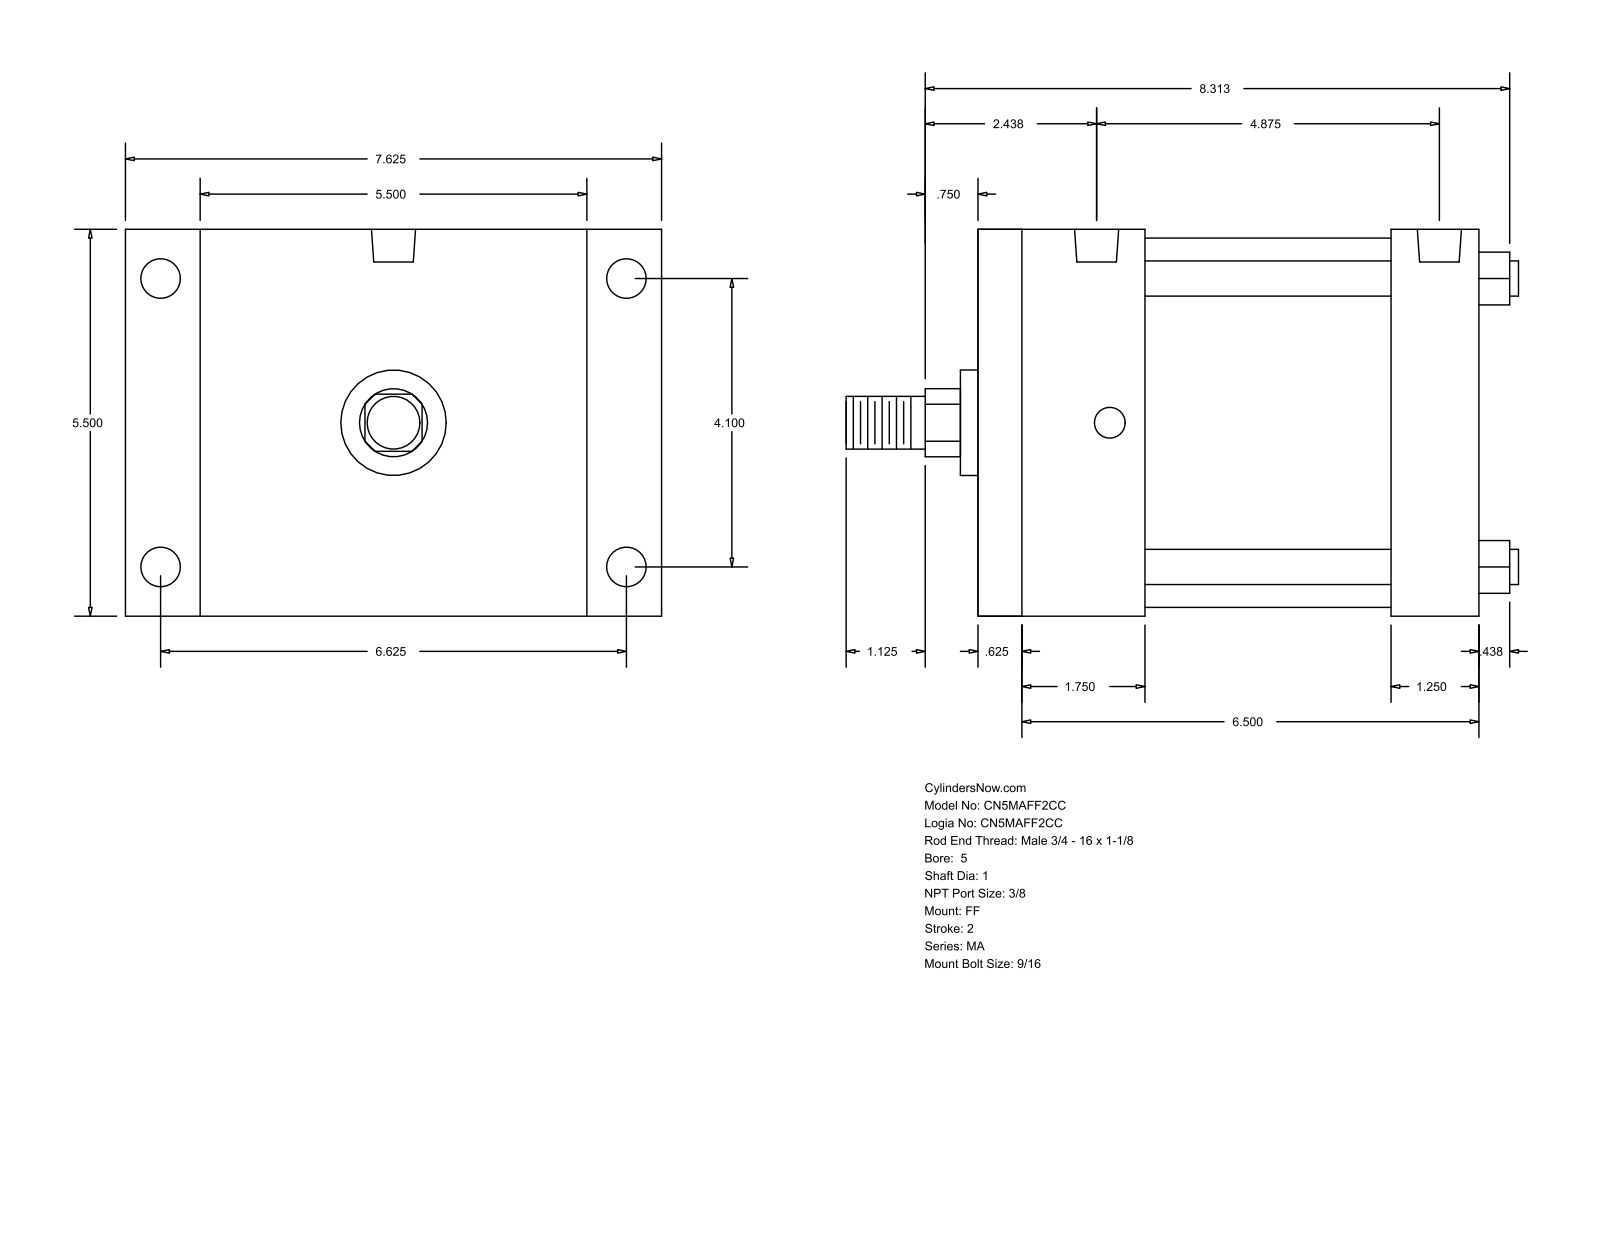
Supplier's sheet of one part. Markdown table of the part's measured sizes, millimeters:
| quantity | value |
| --- | --- |
| part name | MA_FF__0500_1 |
| STEP written by | GSSL Pune (CONFIG_CONTROL_DESIGN) |
| units | millimeters |
| bodies | 0 solids, 92 faces (64 planar, 28 cylindrical, 0 other) |
| overall size | 242.89 × 193.68 × 139.7 |
| round holes (diameter × count) | 11.11 × 4, 14.29 × 4, 15.93 × 2 |
| round bosses / shafts (diameter × count) | 12.7 × 4, 133.35 × 1, 38.1 × 1, 25.4 × 1, 19.05 × 1 |
| partial cylindrical surfaces (radius × count) | 12.29 × 1 |
| main face-to-face distances | 139.7, 180.98, 15.87, 165.11, 149.23, 133.36, 31.75, 60.33, 44.46, 88.9 |
| hole center spacings | 104.14, 114.3, 168.28, 197.9, 4.76, 4.77, 119.06, 119.07 |
